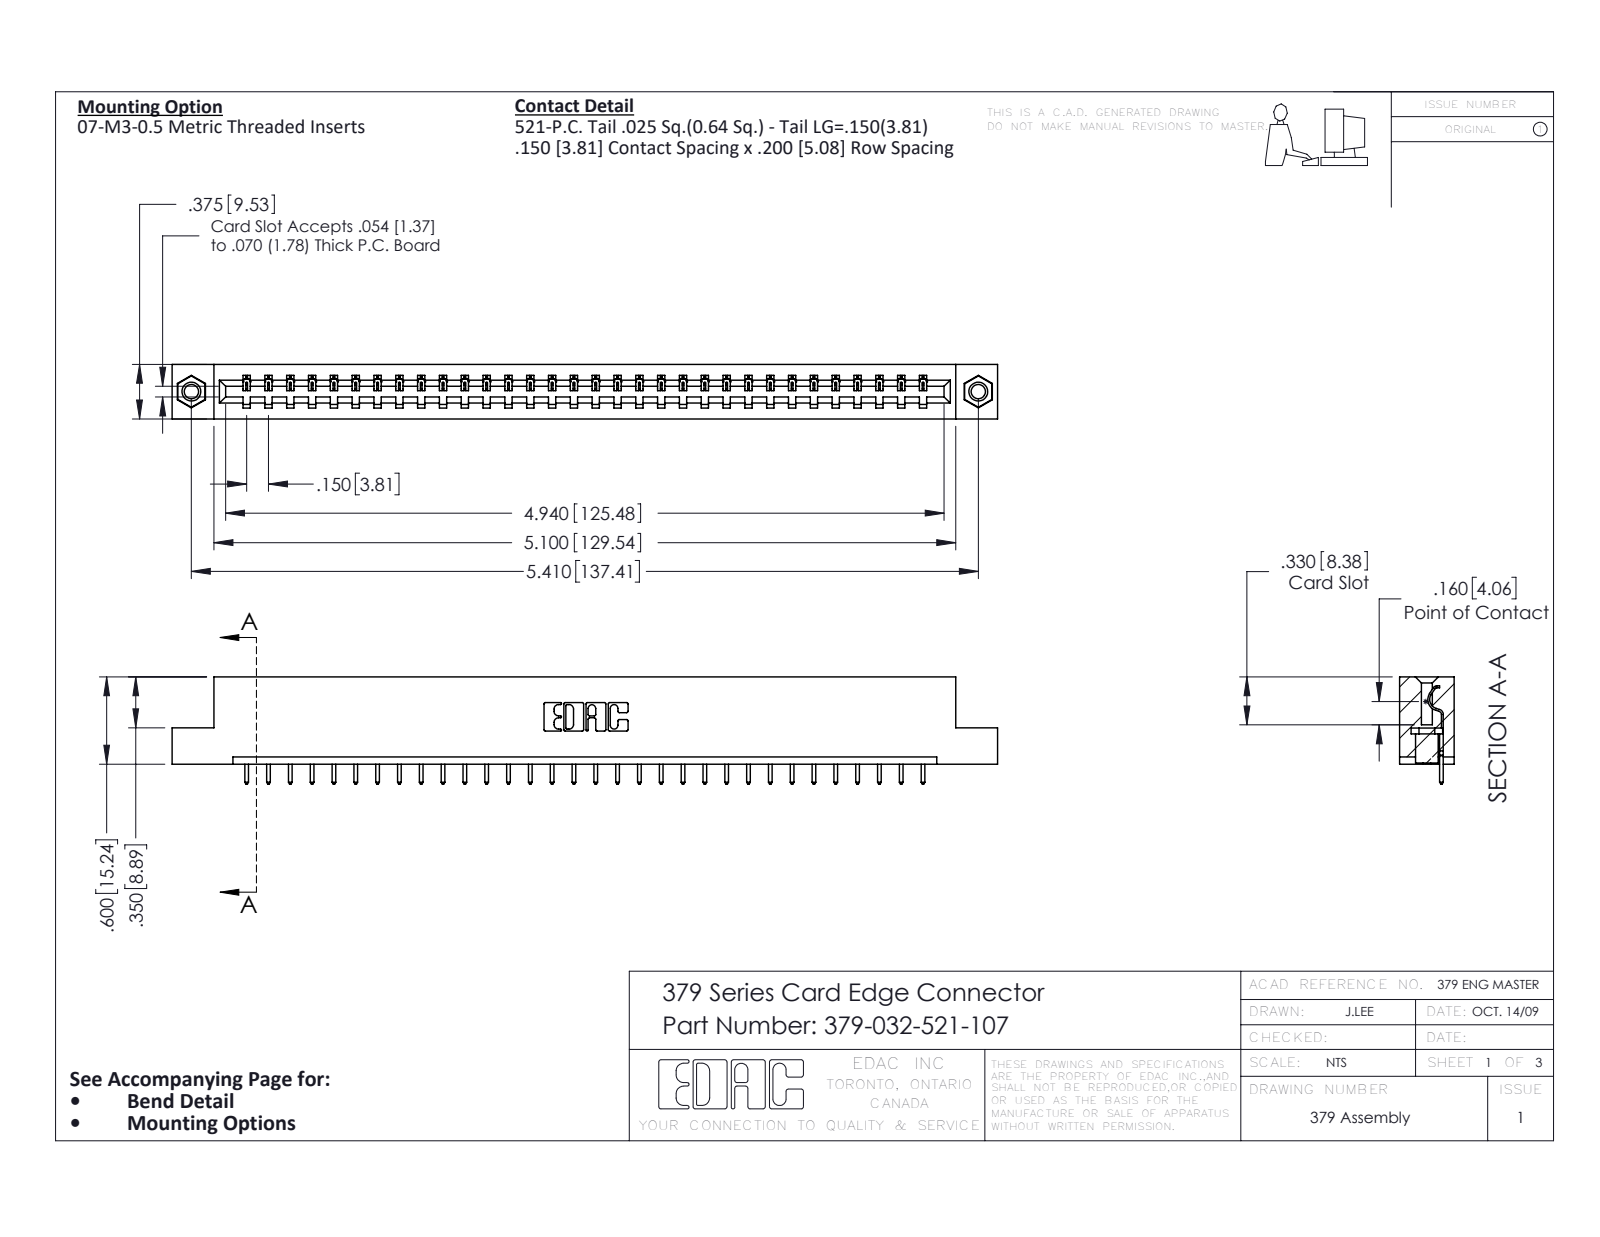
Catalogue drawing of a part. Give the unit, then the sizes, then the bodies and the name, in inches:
Units: inches
Overall size (bounding box): 5.675 × 0.737 × 0.375
Round holes (diameter × count): ⌀0.098 ×2, ⌀0.125 ×2, ⌀0.156 ×2
Round bosses / shafts (diameter × count): ⌀0.155 ×2
Partial cylindrical surfaces — rounded edges, fillets, slot ends (radius × count): R0.006 ×64, R0.01 ×64, R0.01 ×22, R0.007 ×6, R0.031 ×6, R0.026 ×3, R0.014 ×1, R0.022 ×1
Main face-to-face distances: 0.3, 0.075, 0.375, 0.225, 0.6, 0.2, 0.275, 0.1, 0.025, 0.55
Hole centre spacings: 5.41
Volume: 0.91 in³ · Surface area: 23.05 in²
Bodies: 35 solids, 2030 faces (1446 planar, 568 cylindrical, 16 other)
Part name (STEP PRODUCT): 379-032-521-107; 345-292-001_345-293-121; 379 Part_Flush - .156 Dia - TI; 345-250-001_345-250-005-103
STEP written by: SolidWorks 2016 (CONFIG_CONTROL_DESIGN)
